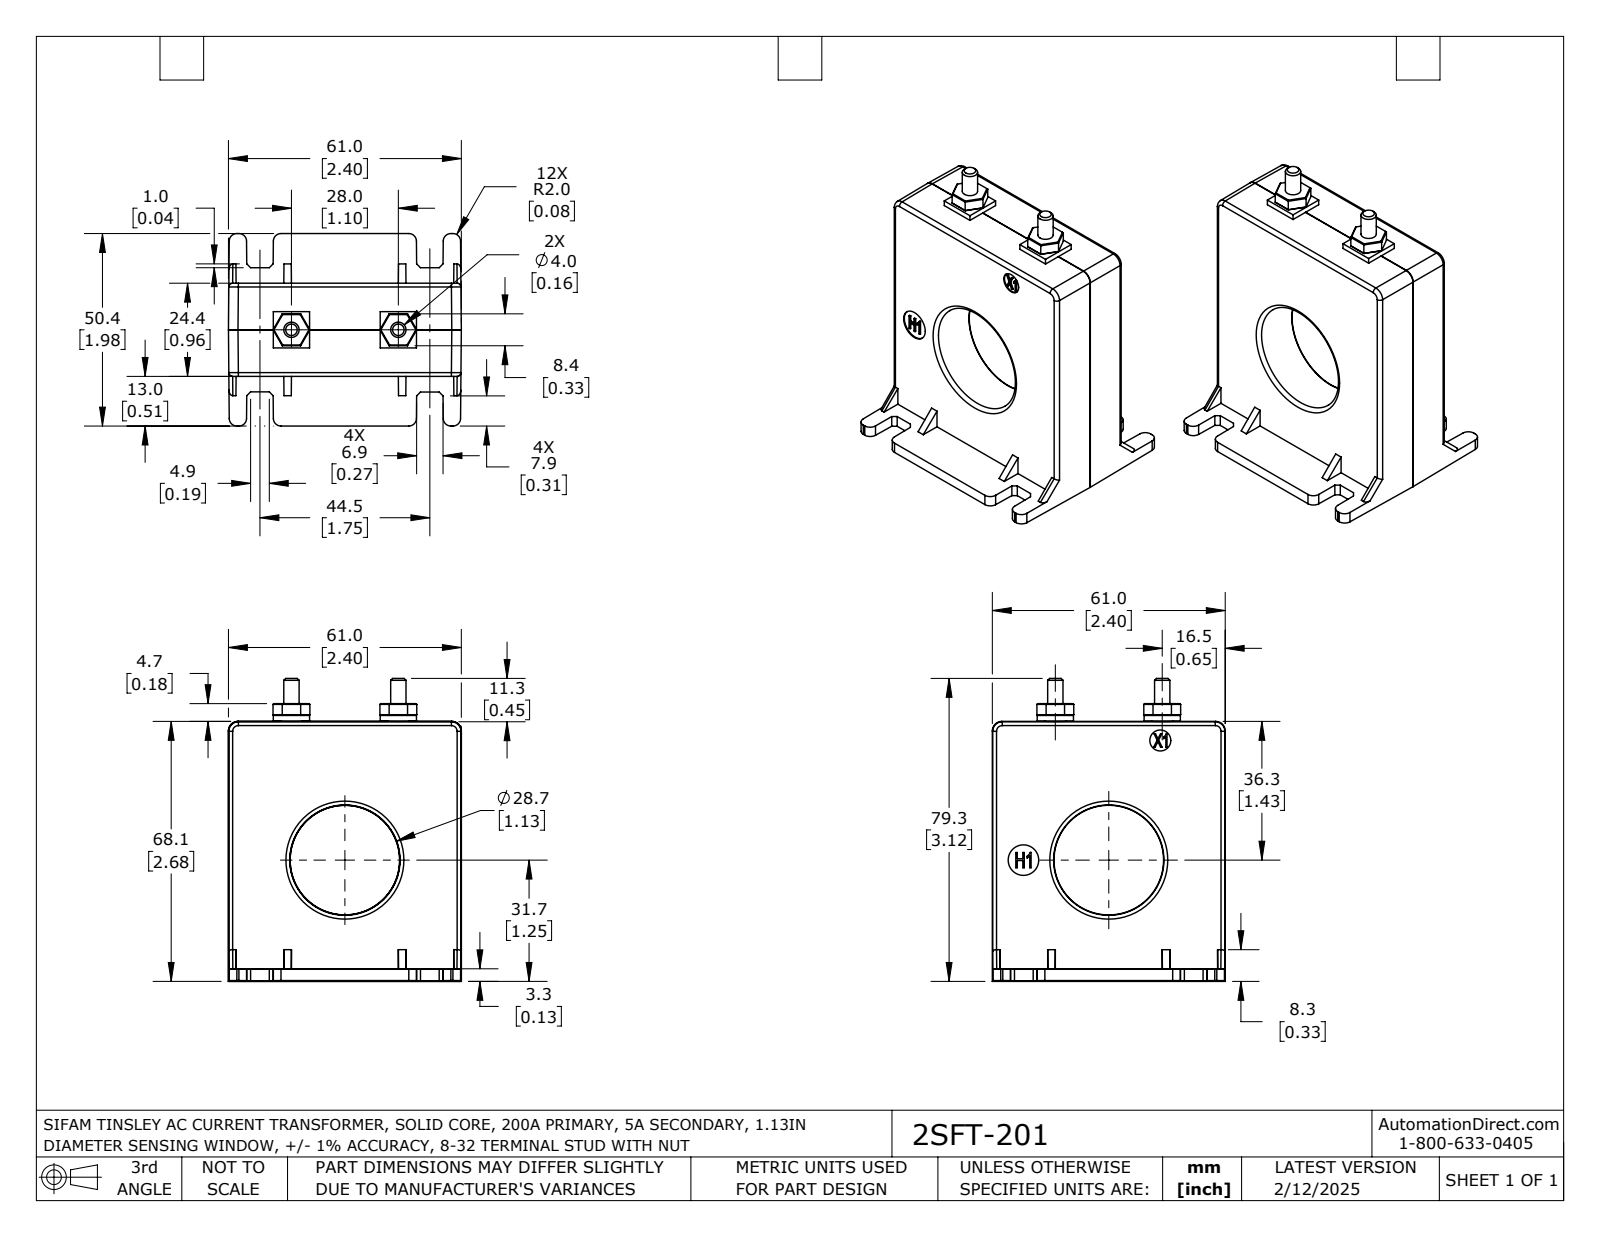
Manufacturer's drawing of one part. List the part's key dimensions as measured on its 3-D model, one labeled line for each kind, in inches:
Part name (STEP PRODUCT): 2SFT-201
STEP written by: SolidWorks 2021 (AUTOMOTIVE_DESIGN)
Units: inches
Bodies: 1 solid, 245 faces (183 planar, 38 cylindrical, 24 other)
Overall size (bounding box): 3.123 × 2.402 × 1.984
Volume: 5.469 in³ · Surface area: 40.07 in²
Round holes (diameter × count): ⌀0.217 ×1, ⌀0.315 ×1
Round bosses / shafts (diameter × count): ⌀0.217 ×2, ⌀0.158 ×2
Partial cylindrical surfaces — rounded edges, fillets, slot ends (radius × count): R0.079 ×12, R0.039 ×10, R0.098 ×4
Main face-to-face distances: 0.48, 0.476, 0.484, 0.961, 2.402, 0.134, 2.68, 2.546, 0.512, 0.992
Hole centre spacings: 1.874
